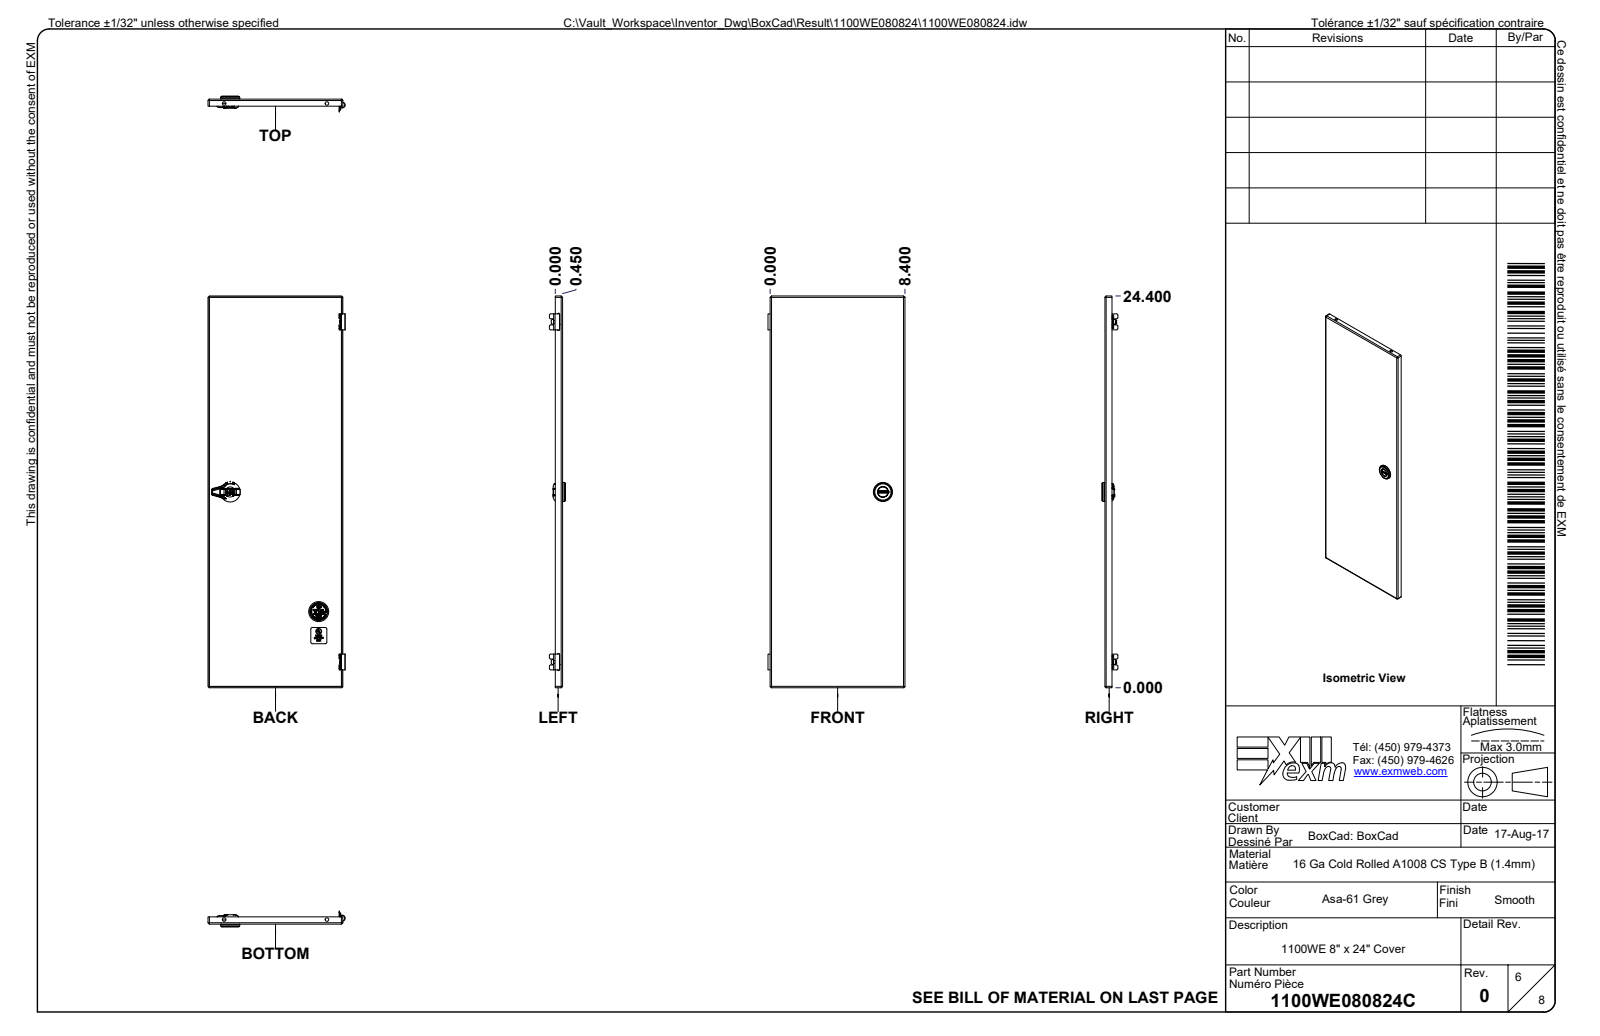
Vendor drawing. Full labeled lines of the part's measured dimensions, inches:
Part name (STEP PRODUCT): 1100WE080824; 1100WE080824B; 1100WE080824B-P; 1100WE080824C (+8 more)
STEP written by: Autodesk Inventor 2024 (AUTOMOTIVE_DESIGN)
Units: inches
Bodies: 8 solids, 3679 faces (1971 planar, 617 cylindrical, 1091 other)
Overall size (bounding box): 24.4 × 8.544 × 8.249
Volume: 53.29 in³ · Surface area: 1 973 in²
Round holes (diameter × count): ⌀0.875 ×5, ⌀1.125 ×5, ⌀0.29 ×4, ⌀0.03 ×2, ⌀0.177 ×2, ⌀0.043 ×1, ⌀0.375 ×1, ⌀1.063 ×1
Round bosses / shafts (diameter × count): ⌀1.125 ×5, ⌀0.875 ×5, ⌀1.26 ×1, ⌀1.25 ×1, ⌀1.181 ×1, ⌀1.142 ×1, ⌀0.787 ×1, ⌀0.312 ×1
Partial cylindrical surfaces — rounded edges, fillets, slot ends (radius × count): R0.01 ×219, R0.031 ×22, R0.02 ×19, R0.079 ×18, R0.086 ×14, R0.084 ×8, R0.009 ×7, R0.039 ×4
Main face-to-face distances: 0.055, 7.945, 8, 7.89, 0.053, 8.015, 8.068, 7.96, 8.013, 23.945
Hole centre spacings: 6, 6.419, 10.298, 12, 15.585, 21.254, 22, 22.804
